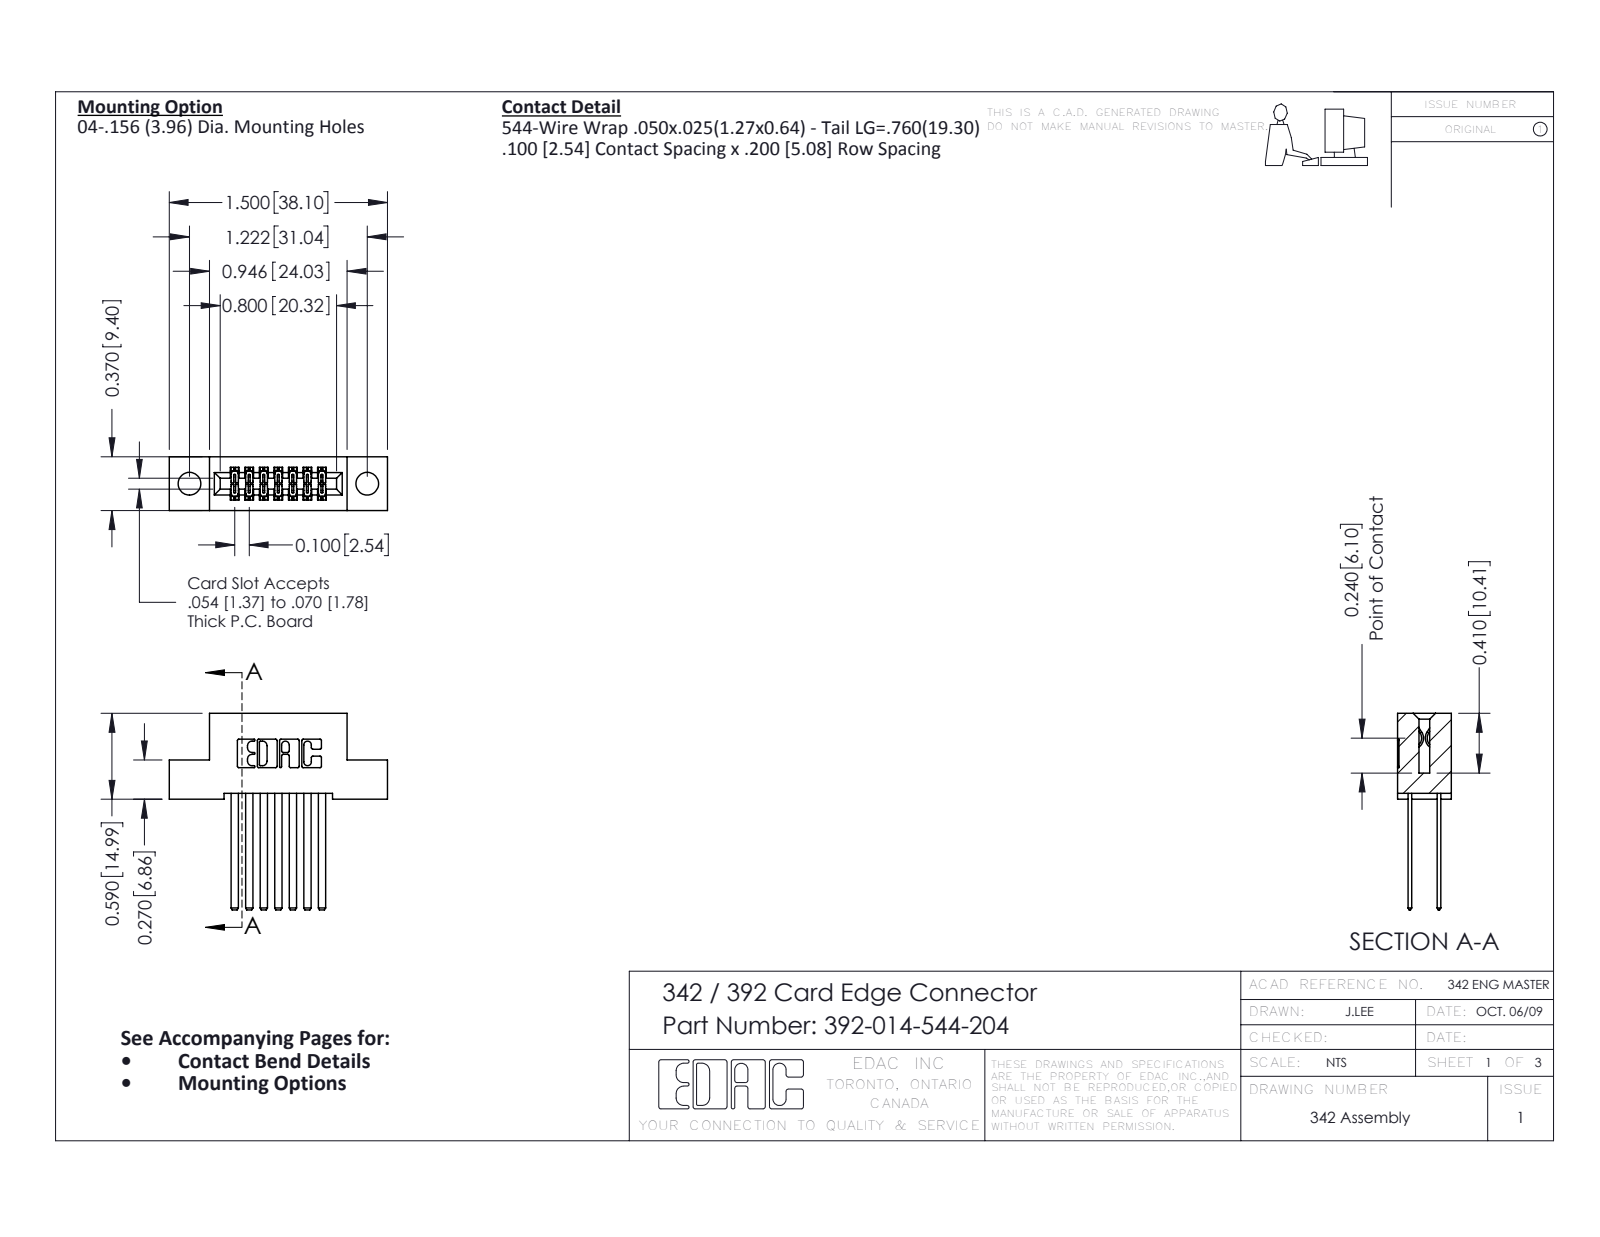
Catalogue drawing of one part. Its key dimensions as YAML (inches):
part_name: "342 Part_.156 TH; 392-014-544-204; 345-292-001_345-293-144"
step_written_by: "SolidWorks 2016 (CONFIG_CONTROL_DESIGN)"
units: inches
bodies: {solids: 15, faces: 754, planar: 514, cylindrical: 240, other: 0}
overall_size: [1.5, 1.35, 0.37]
volume: 0.205
surface_area: 7.728
round_holes:
  - {diameter: 0.156, count: 2}
partial_cylinders:
  - {radius: 0.01, count: 22}
  - {radius: 0.006, count: 21}
  - {radius: 0.007, count: 6}
  - {radius: 0.031, count: 6}
  - {radius: 0.026, count: 3}
  - {radius: 0.014, count: 2}
  - {radius: 0.022, count: 2}
  - {radius: 0.024, count: 2}
face_to_face_distances: [0.2, 0.072, 0.298, 0.1, 0.098, 0.272, 0.025, 0.04, 0.37, 0.225]
hole_center_spacings: [1.222]
